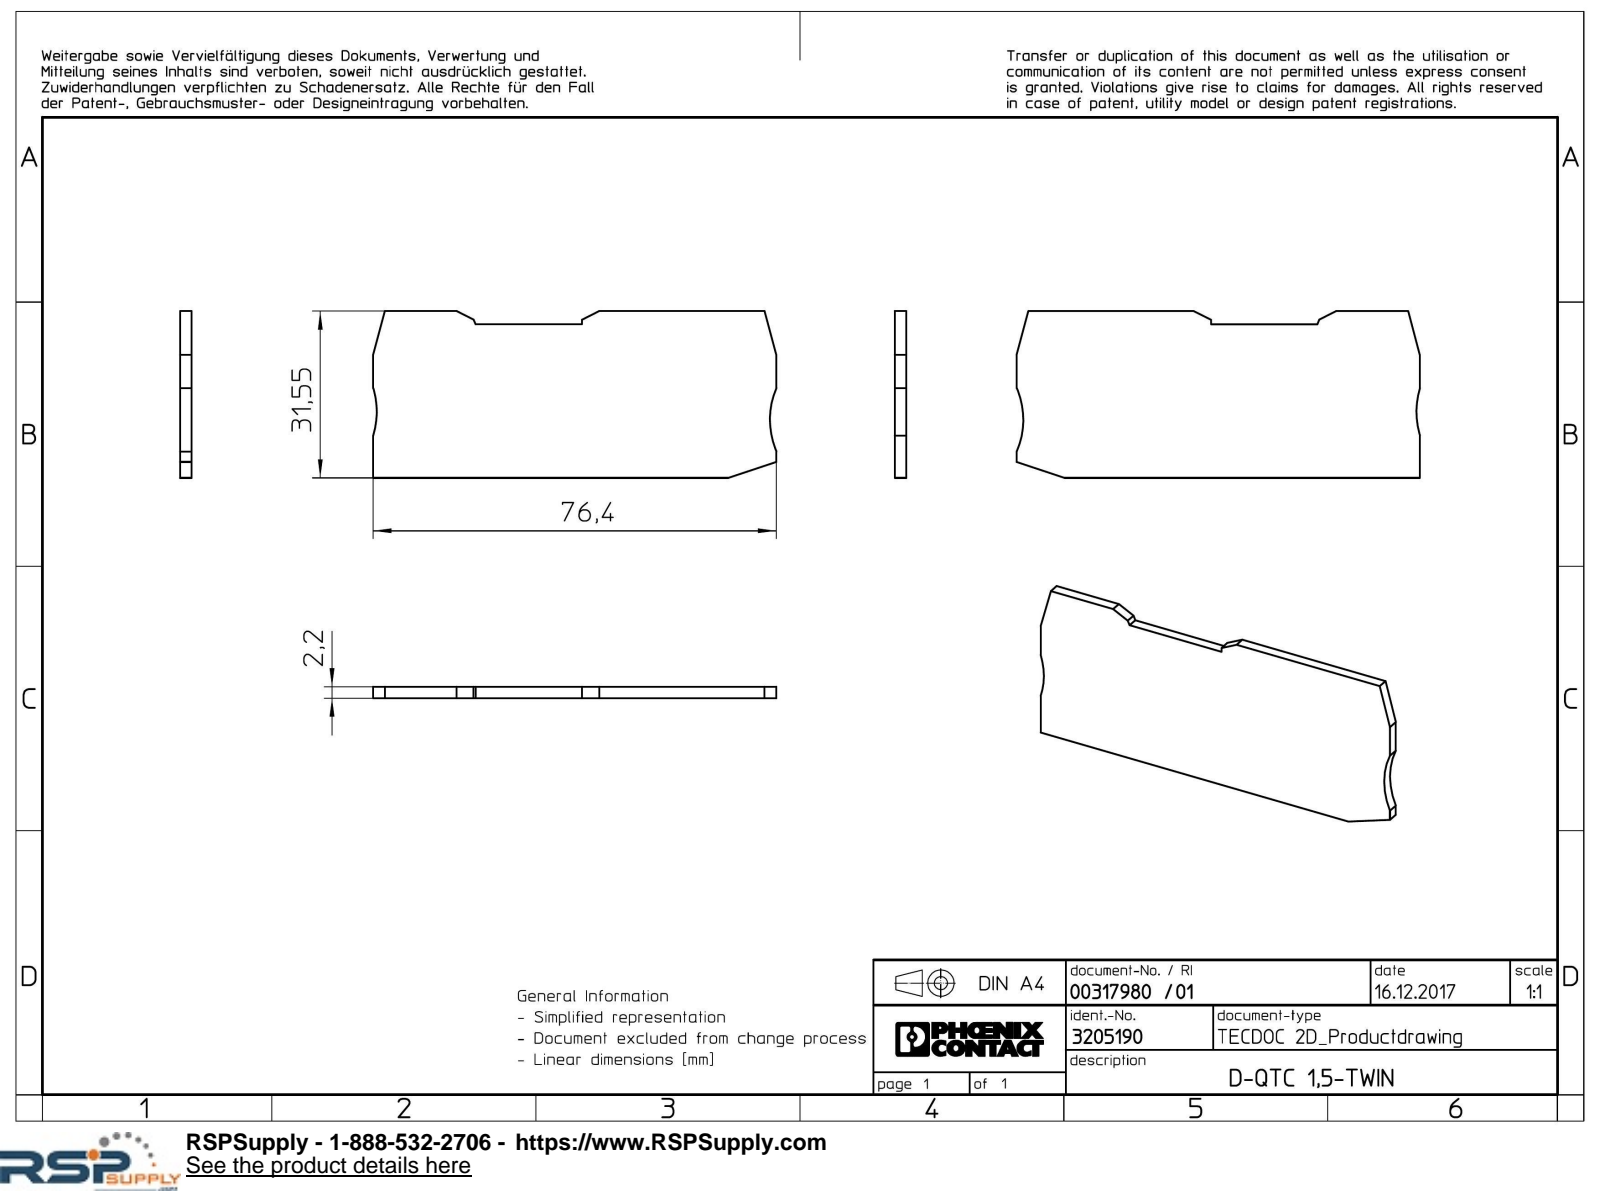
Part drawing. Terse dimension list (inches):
name: D-QTC_1.5-TWIN-select
written by: Creo Elements/Direct Modeling 18.1I 14-Aug-2016 (C) Parametric Technology GmbH (AUTOMOTIVE_DESIGN)
unit: in
bodies: 1 solid, 19 faces (17 planar, 2 cylindrical, 0 other)
size: 3.008 × 1.242 × 0.087
volume: 0.31 in³; area: 7.877 in²
rounds: 2× R0.591
face distances: 0.087, 1.242, 1.144, 0.098, 3.008, 1.557, 1.451
